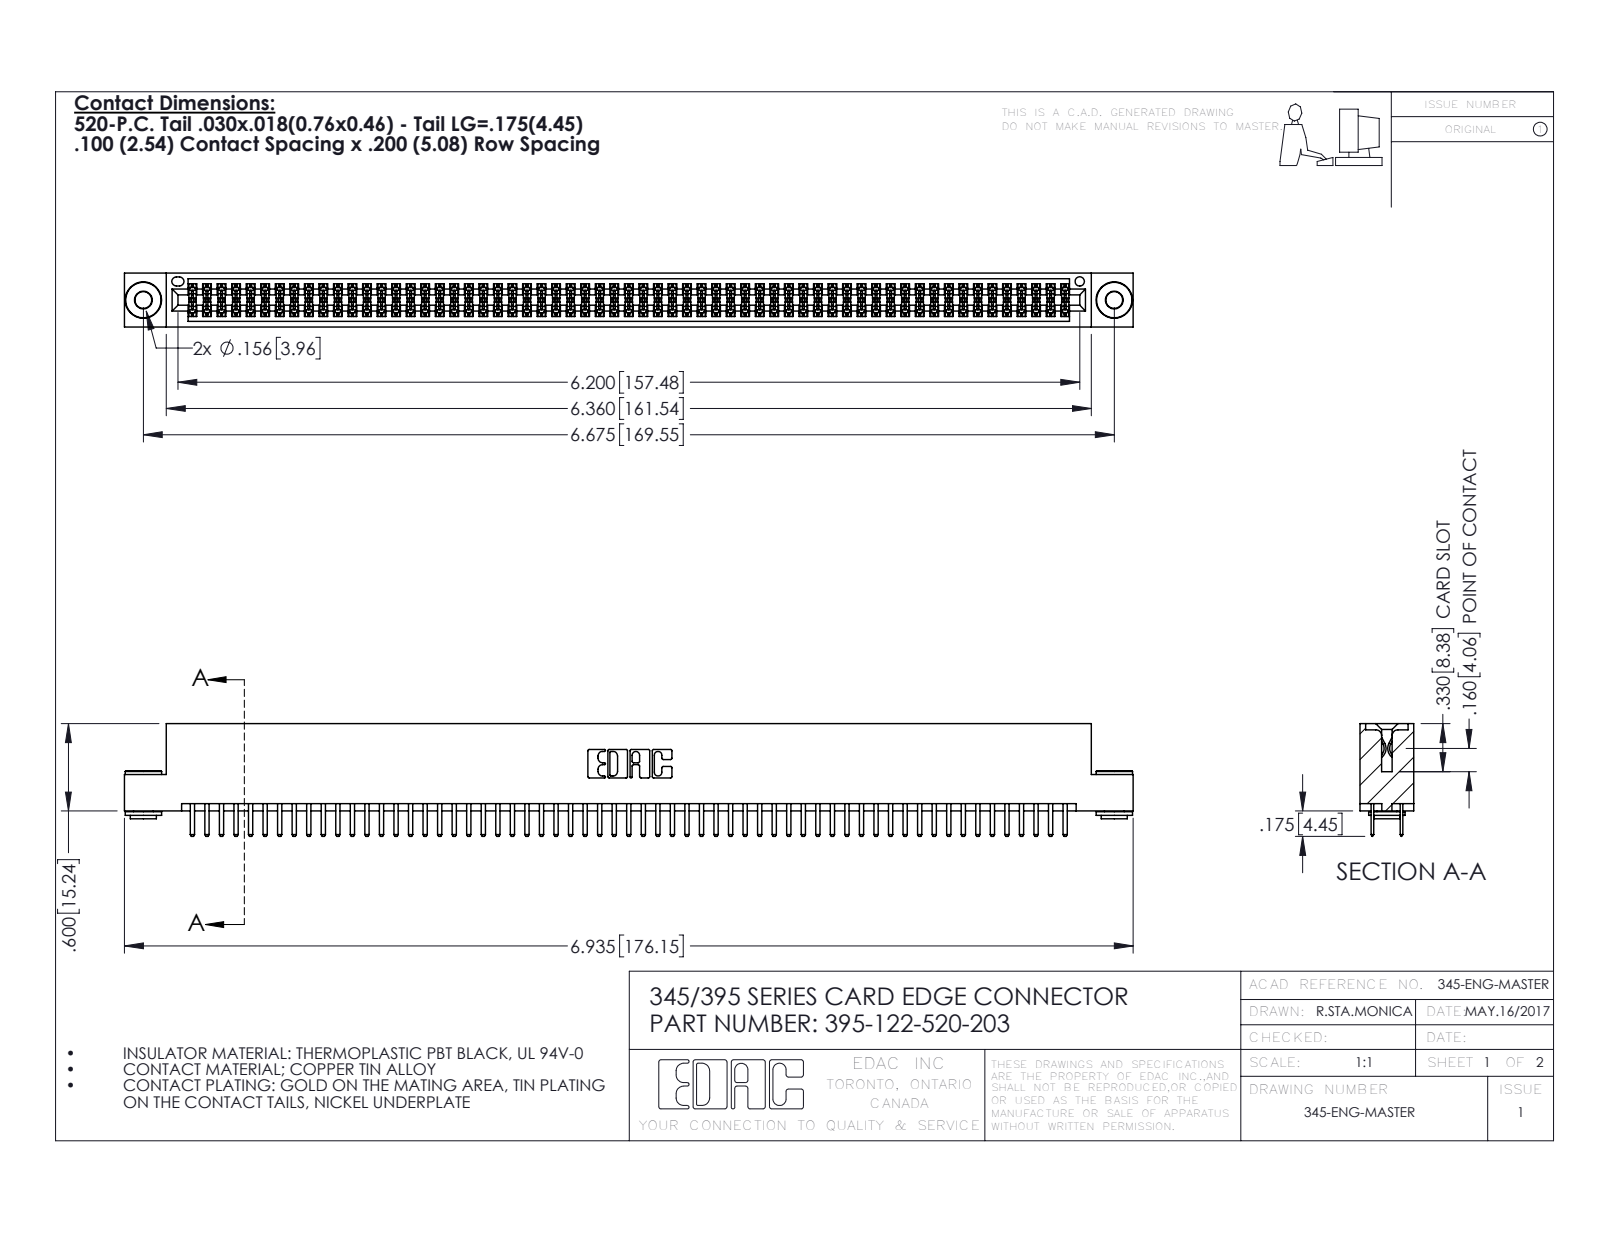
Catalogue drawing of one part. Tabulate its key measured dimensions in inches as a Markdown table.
| quantity | value |
| --- | --- |
| part name | 345 Part_Flush Mounting Lugs - 0.156 Dia-TH; 345-292-001_345-293-120; 395-122-520-203; 345-250-002_345-250-002-102 |
| STEP written by | SolidWorks 2016 (CONFIG_CONTROL_DESIGN) |
| units | inches |
| bodies | 125 solids, 6752 faces (4360 planar, 2384 cylindrical, 8 other) |
| overall size | 6.935 × 0.775 × 0.37 |
| volume | 1.053 in³ |
| surface area | 40.24 in² |
| round holes (diameter × count) | 0.116 × 2, 0.156 × 2, 0.064 × 1 |
| round bosses / shafts (diameter × count) | 0.25 × 2, 0.18 × 2, 0.136 × 2 |
| partial cylindrical surfaces (radius × count) | 0.006 × 183, 0.01 × 126, 0.01 × 22, 0.007 × 6, 0.031 × 6, 0.026 × 3, 0.014 × 2, 0.019 × 2 |
| main face-to-face distances | 0.072, 0.298, 0.2, 0.37, 0.025, 0.098, 0.272, 0.225, 0.022, 0.072 |
| hole center spacings | 0.27, 6.439, 6.675 |
